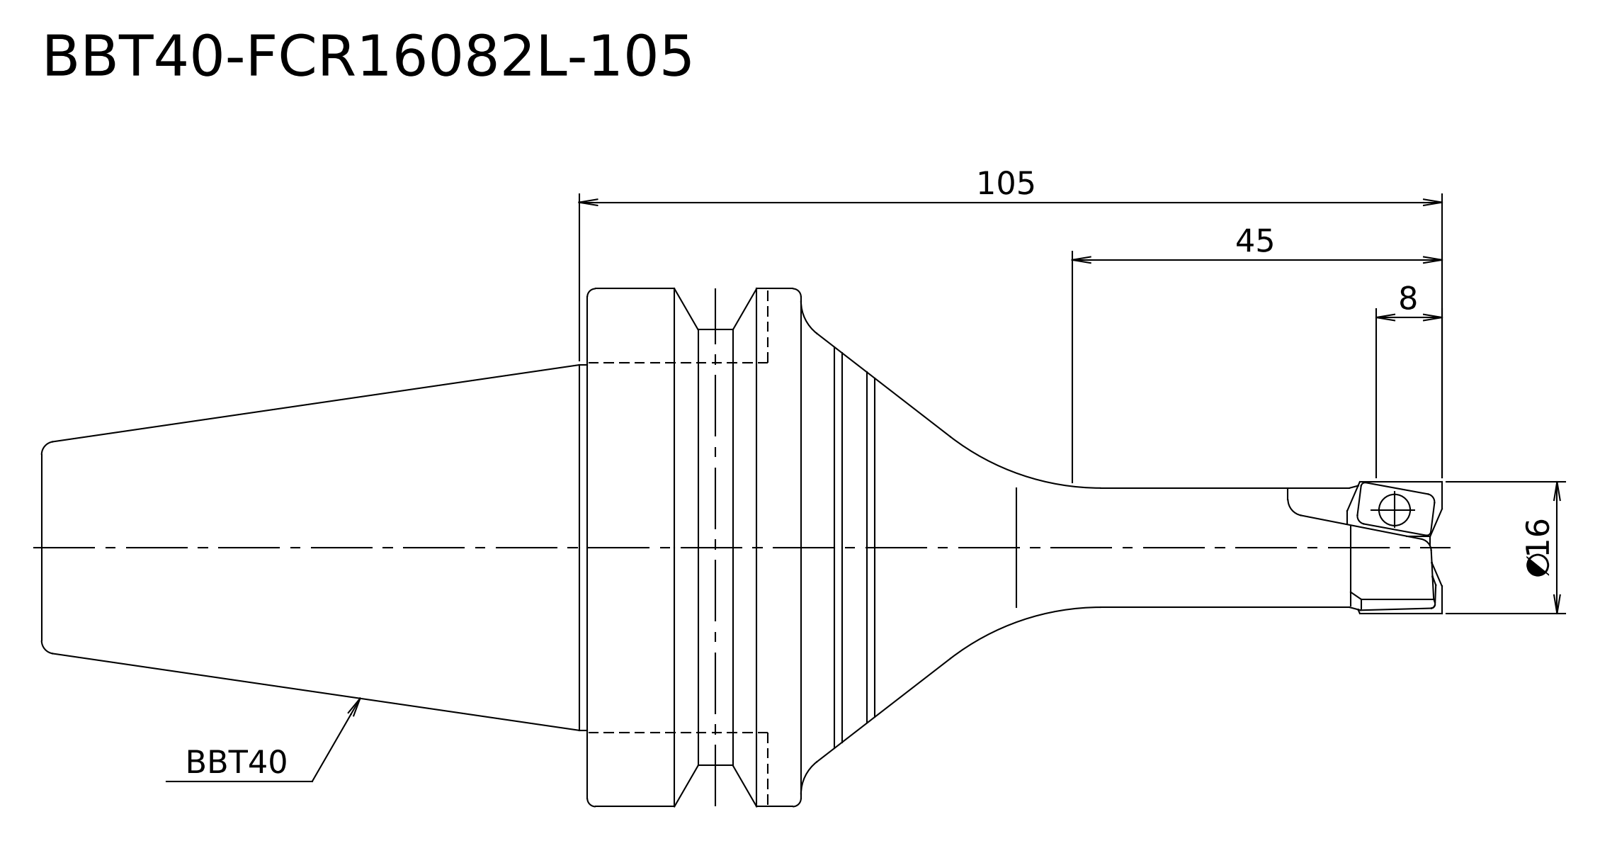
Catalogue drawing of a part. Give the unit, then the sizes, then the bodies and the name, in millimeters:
Units: millimetres
Overall size (bounding box): 170.4 × 63 × 63
Round bosses / shafts (diameter × count): ⌀63 ×1, ⌀53 ×1, ⌀44.45 ×1, ⌀16 ×1, ⌀14.5 ×1
Main face-to-face distances: 66.4, 26, 92.4, 78, 104, 170.4
Volume: 179 190 mm³ · Surface area: 22 452 mm²
Bodies: 1 solid, 17 faces (4 planar, 6 cylindrical, 7 other)
STEP written by: Kubotek KeyCreator V8.5.1 (14335) (CONFIG_CONTROL_DESIGN)
